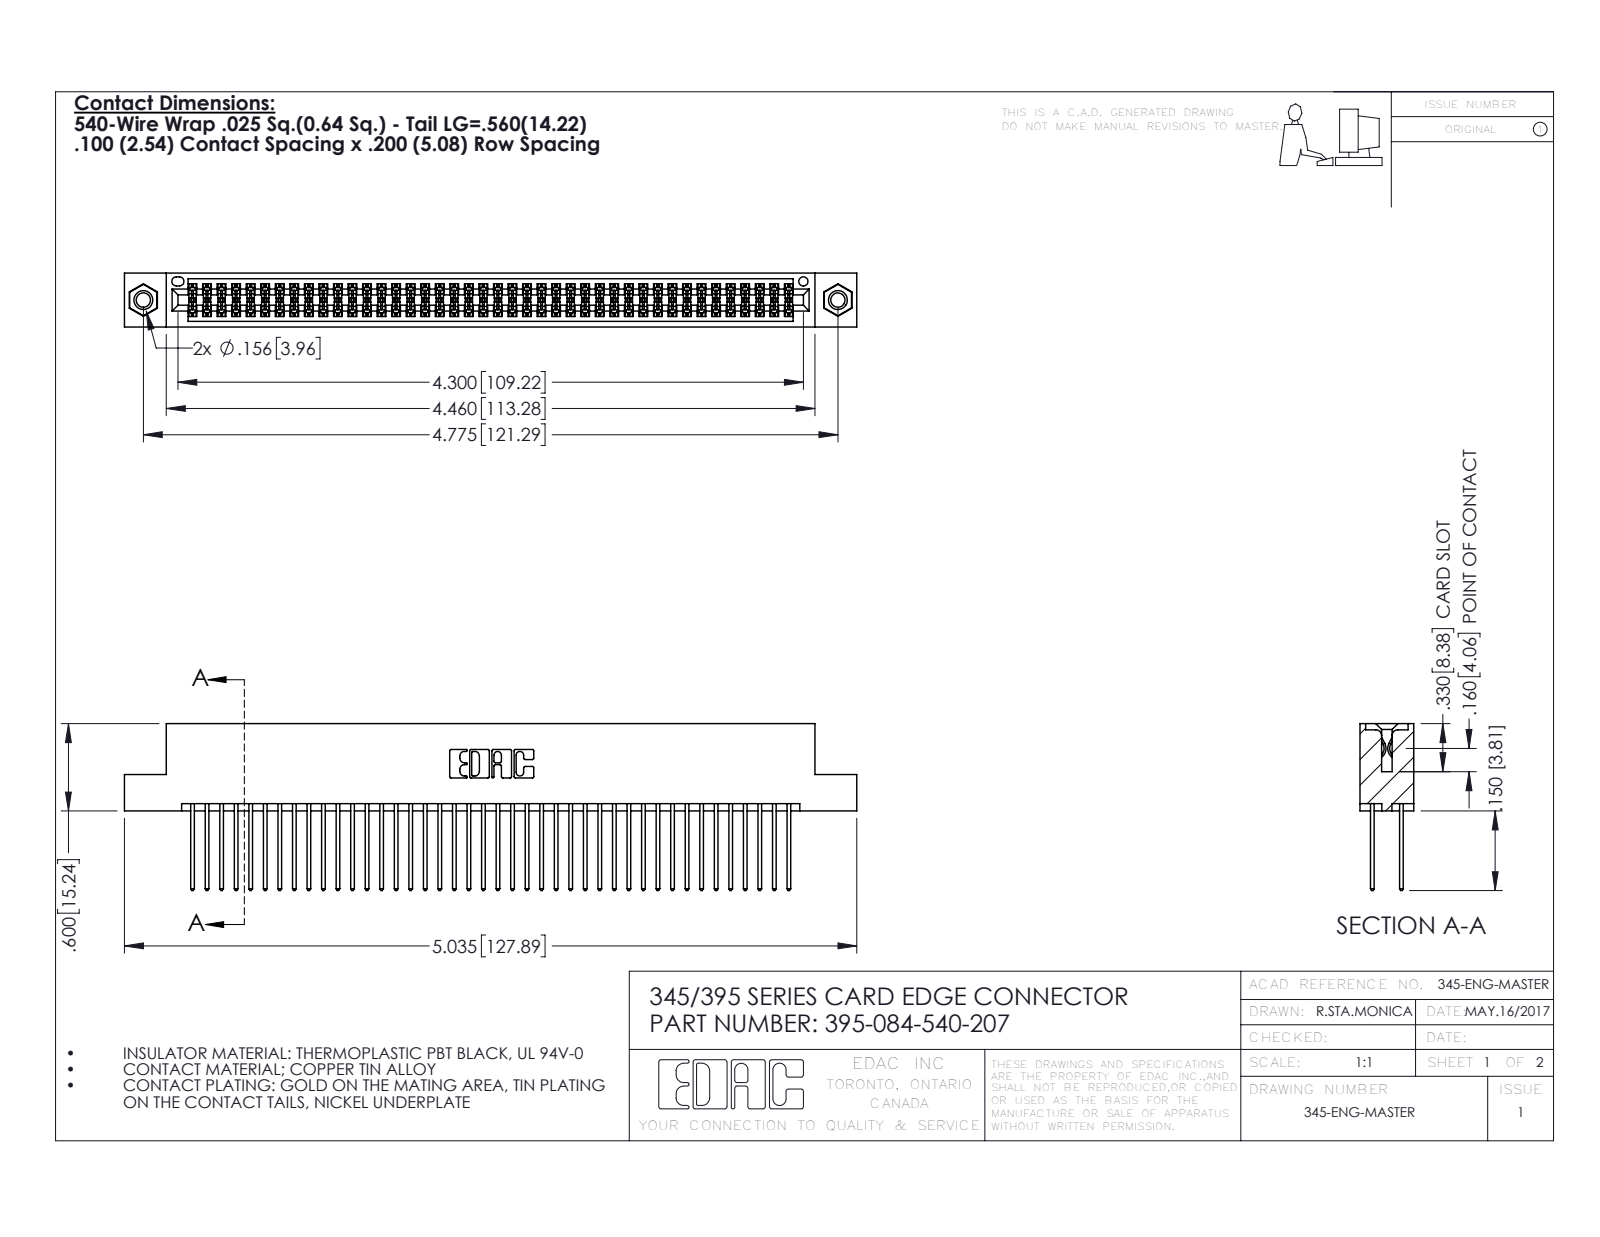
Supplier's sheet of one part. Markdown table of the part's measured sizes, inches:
| quantity | value |
| --- | --- |
| part name | 395-084-540-207; 345-292-001_345-293-140; 345 Part_Flush Mounting Lugs - 0.156 Dia-TI; 345-250-001_345-250-005-103 |
| STEP written by | SolidWorks 2016 (CONFIG_CONTROL_DESIGN) |
| units | inches |
| bodies | 87 solids, 4386 faces (2884 planar, 1486 cylindrical, 16 other) |
| overall size | 5.035 × 1.147 × 0.37 |
| volume | 0.777 in³ |
| surface area | 31.5 in² |
| round holes (diameter × count) | 0.098 × 2, 0.125 × 2, 0.156 × 2, 0.064 × 1 |
| round bosses / shafts (diameter × count) | 0.155 × 2 |
| partial cylindrical surfaces (radius × count) | 0.006 × 126, 0.01 × 84, 0.01 × 22, 0.007 × 6, 0.031 × 6, 0.026 × 3, 0.014 × 2, 0.019 × 2 |
| main face-to-face distances | 0.072, 0.298, 0.2, 0.098, 0.272, 0.025, 0.37, 0.225, 0.175, 0.149 |
| hole center spacings | 0.27, 4.539, 4.775 |
